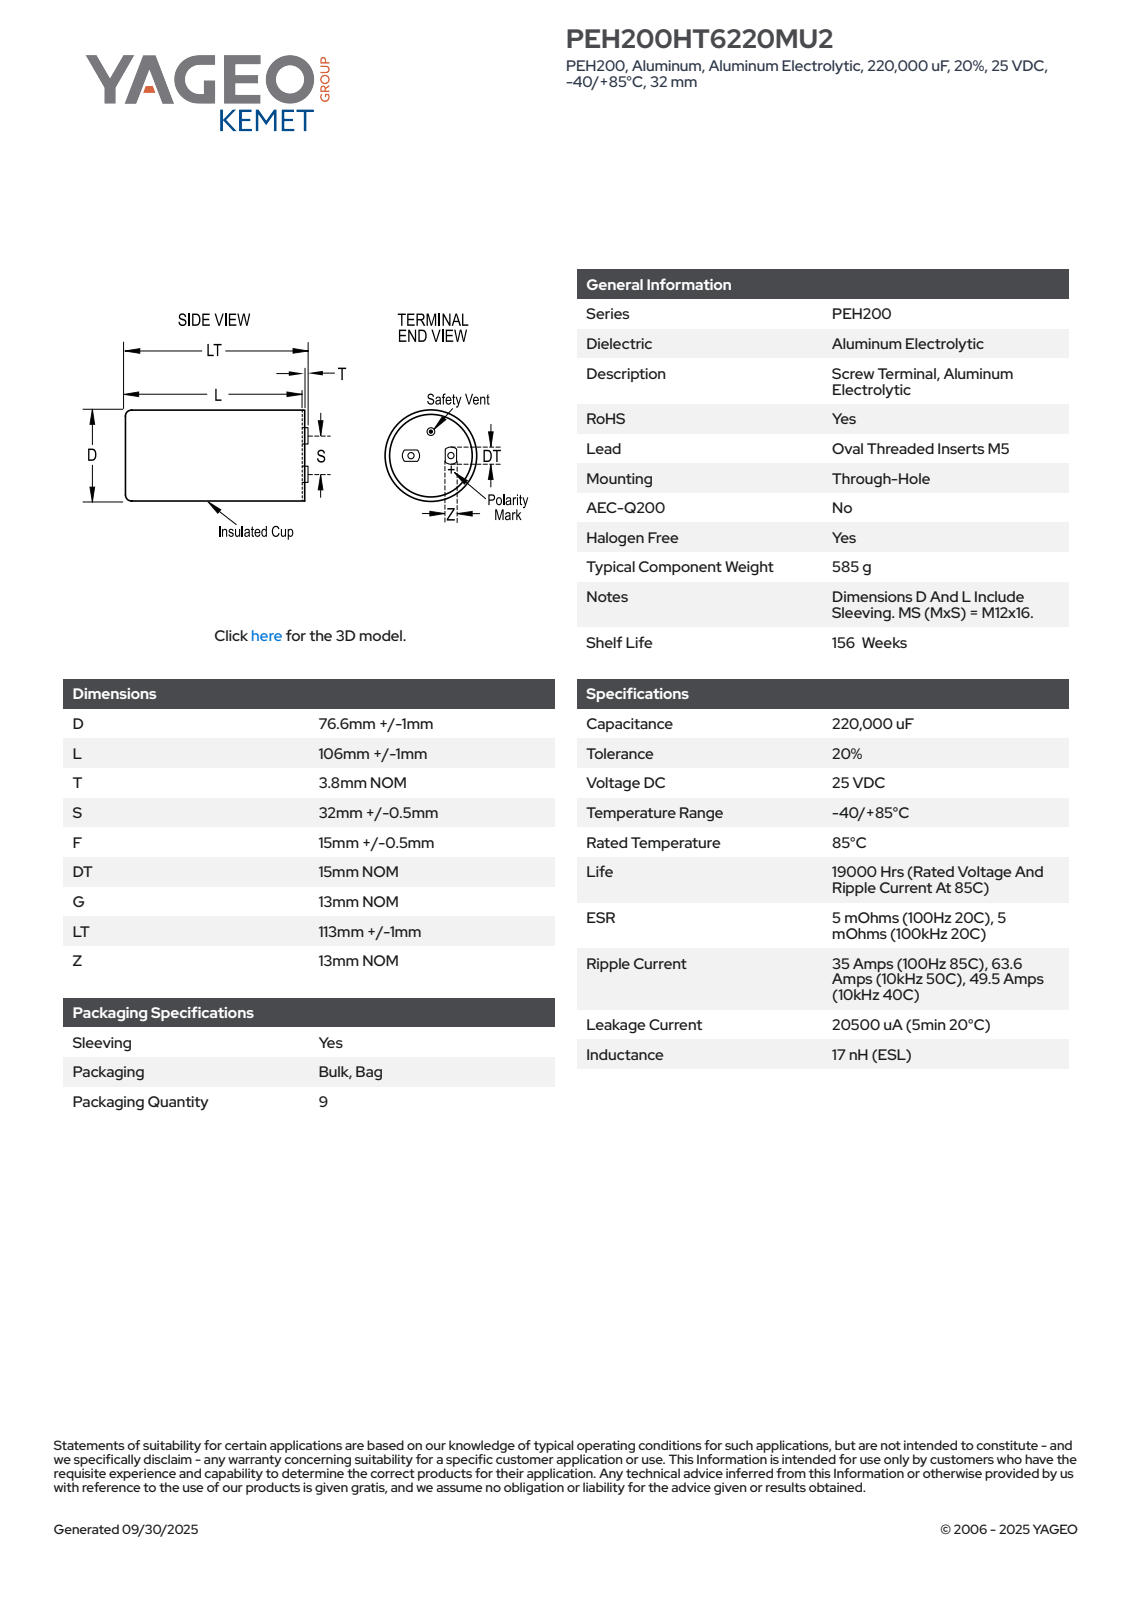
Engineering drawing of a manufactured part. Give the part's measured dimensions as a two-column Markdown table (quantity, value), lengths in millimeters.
| quantity | value |
| --- | --- |
| part name | CARC_D77.6L107S32T3.8; Oval_Terminal_7; Can_7 |
| STEP written by | SolidWorks 2014 (AUTOMOTIVE_DESIGN) |
| units | millimeters |
| bodies | 3 solids, 91 faces (38 planar, 21 cylindrical, 32 other) |
| overall size | 114 × 77.6 × 77.6 |
| volume | 508 549 mm³ |
| surface area | 38 441 mm² |
| round holes (diameter × count) | 4.02 × 2, 75.6 × 1 |
| round bosses / shafts (diameter × count) | 7.5 × 2, 77.6 × 1 |
| partial cylindrical surfaces (radius × count) | 7.5 × 2, 38.79 × 1 |
| main face-to-face distances | 107, 7, 114, 3.8, 3.2, 110.2, 13, 5, 12, 8.2 |
| hole center spacings | 16, 32 |
